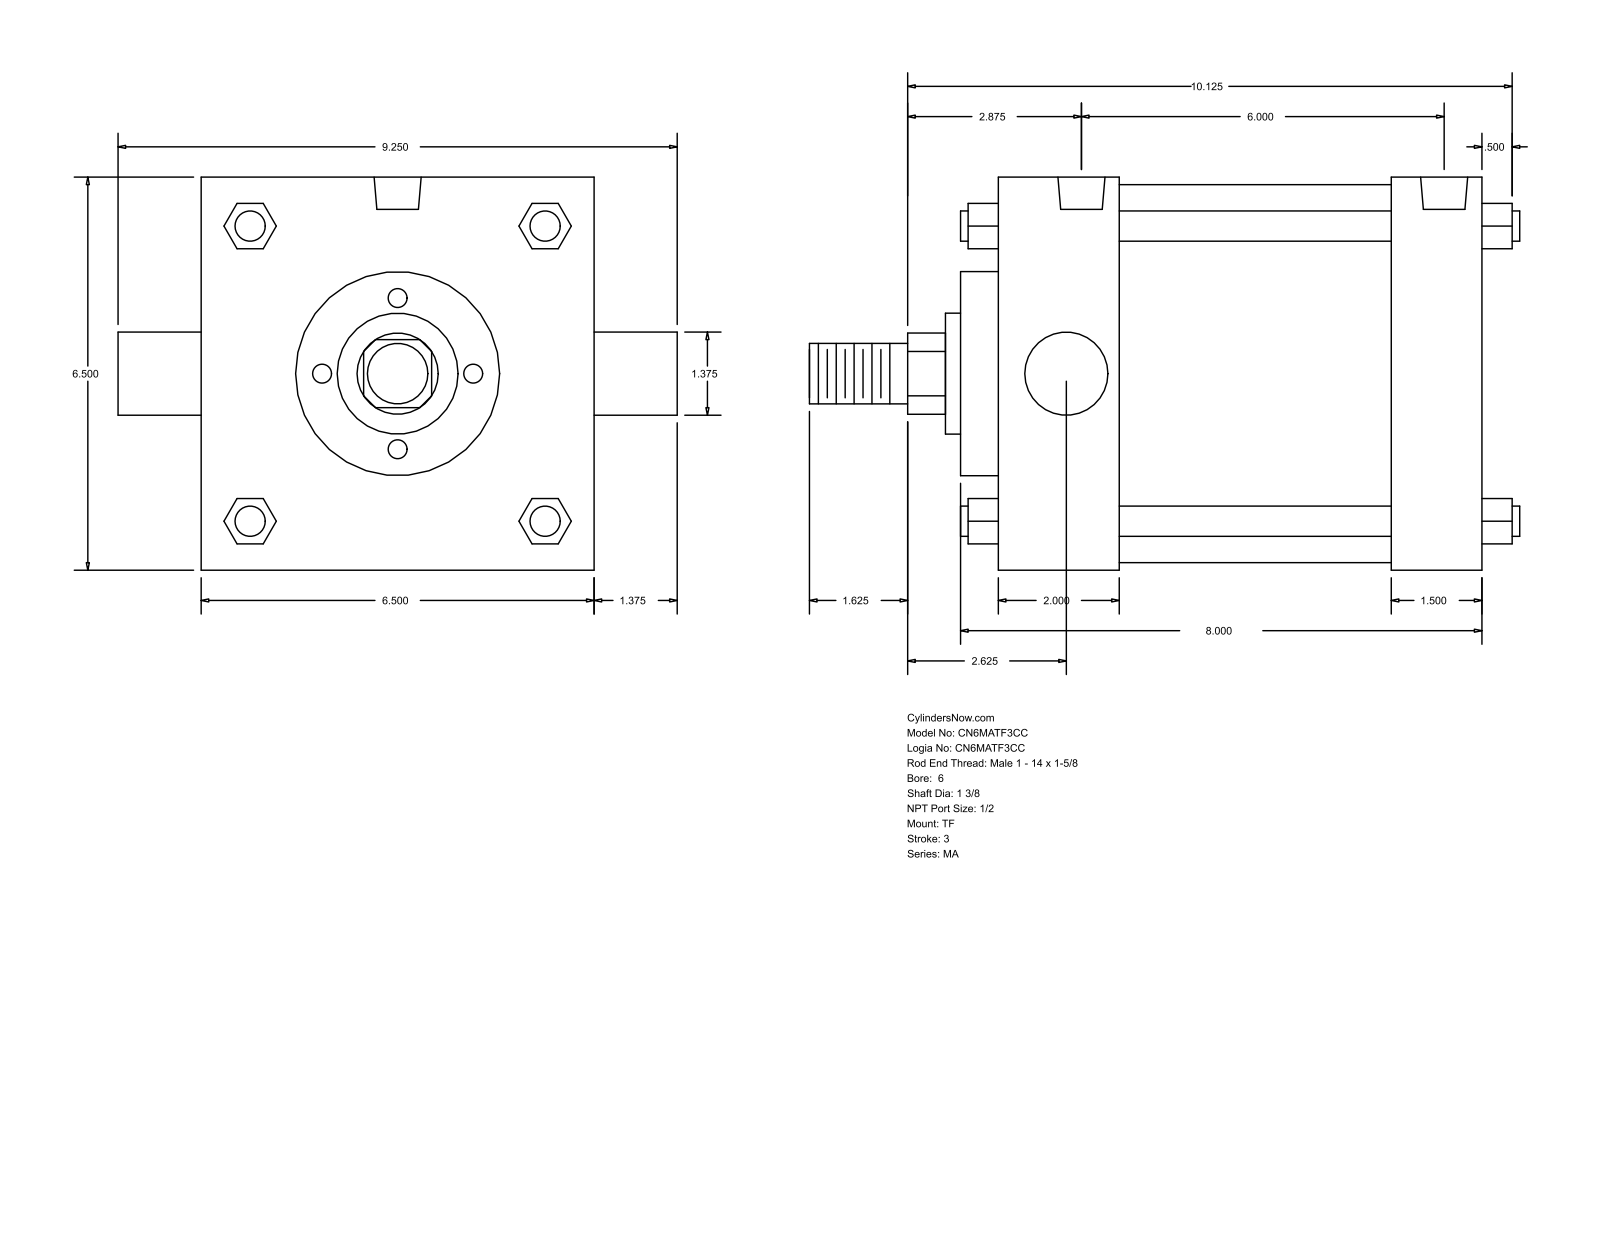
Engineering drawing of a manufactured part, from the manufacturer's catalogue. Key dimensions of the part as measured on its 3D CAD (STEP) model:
Part name (STEP PRODUCT): MA_TF__0600_1.375
STEP written by: GSSL Pune (CONFIG_CONTROL_DESIGN)
Units: millimetres
Bodies: 0 solids, 122 faces (93 planar, 29 cylindrical, 0 other)
Overall size (bounding box): 298.45 × 234.95 × 165.1
Round holes (diameter × count): ⌀17.46 ×3, ⌀19.77 ×2
Round bosses / shafts (diameter × count): ⌀12.7 ×4, ⌀34.92 ×2, ⌀158.75 ×1, ⌀85.72 ×1, ⌀50.8 ×1, ⌀25.4 ×1
Partial cylindrical surfaces — rounded edges, fillets, slot ends (radius × count): R17.06 ×1
Main face-to-face distances: 165.1, 206.37, 50.8, 168.28, 155.57, 117.48, 38.09, 66.67, 15.87, 184.15
Hole centre spacings: 3.18, 152.4, 155.58
